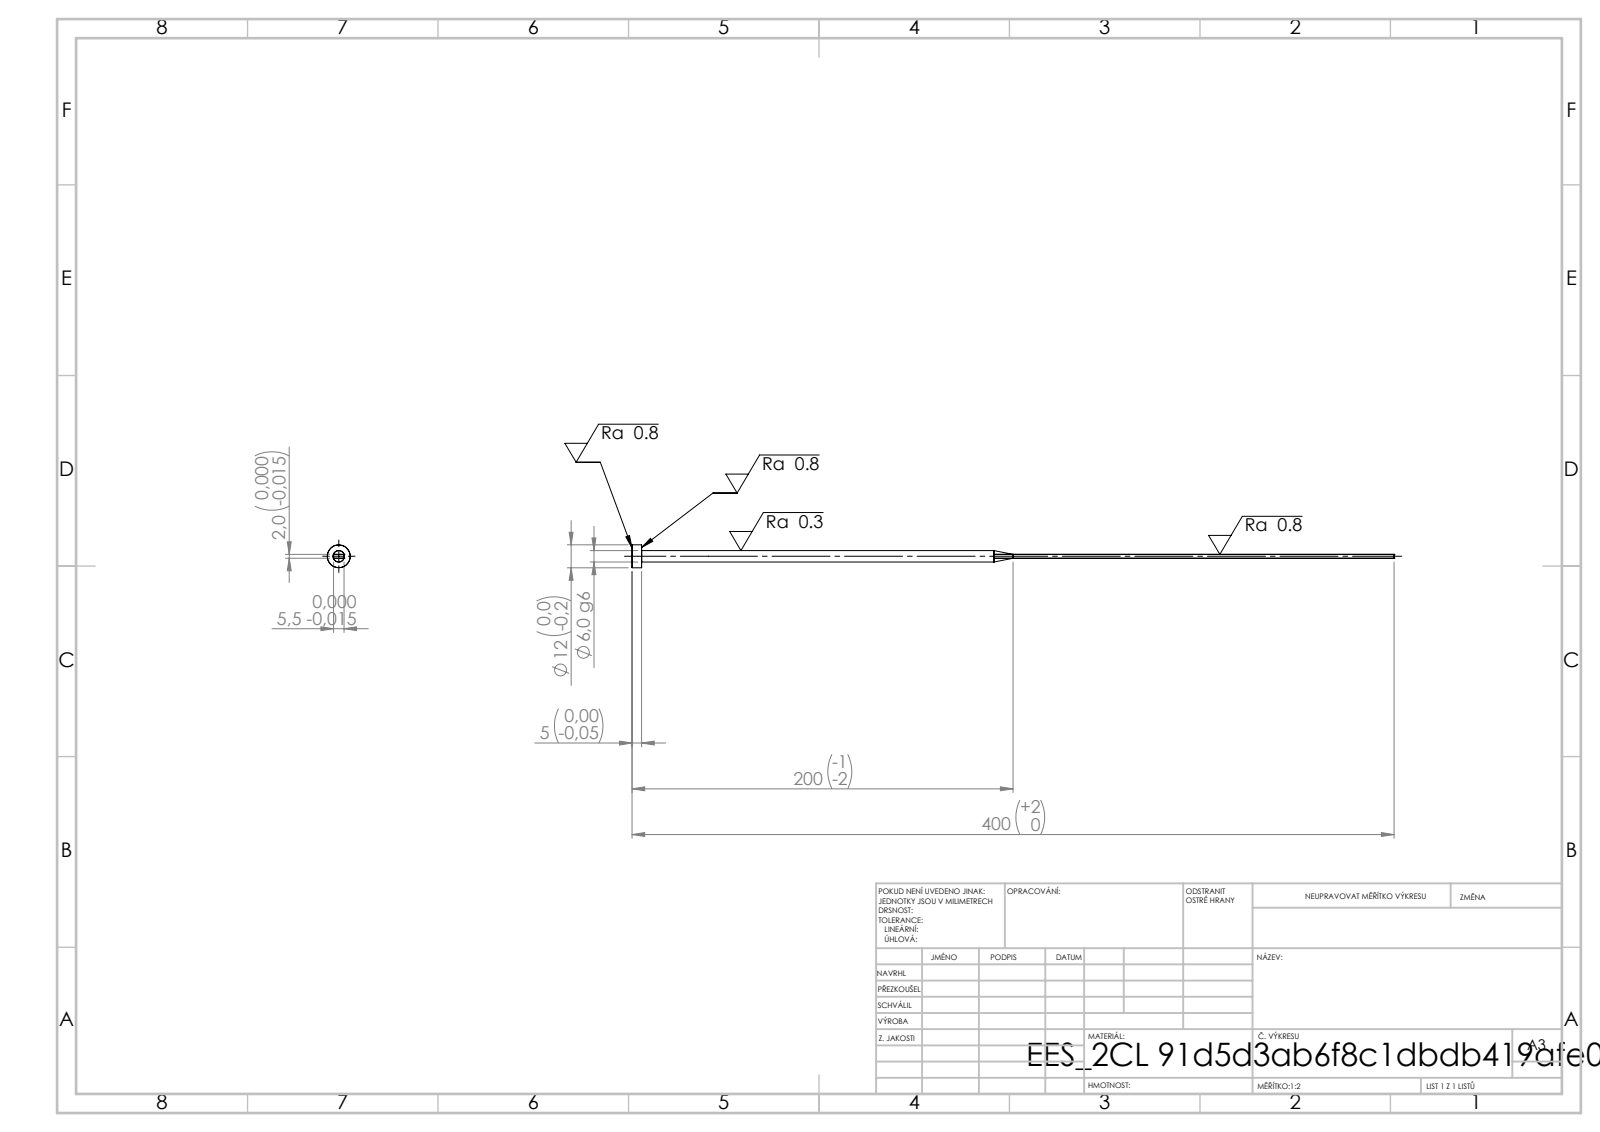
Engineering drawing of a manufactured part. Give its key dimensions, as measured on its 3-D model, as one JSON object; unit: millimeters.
{"step_written_by": "SolidWorks 2019 (CONFIG_CONTROL_DESIGN)", "units": "millimeters", "bodies": {"solids": 1, "faces": 15, "planar": 7, "cylindrical": 4, "other": 4}, "overall_size": [400, 12, 12], "volume_mm3": 8188, "surface_area_mm2": 7050, "round_bosses_or_shafts": [[12, 1], [6, 1]], "face_to_face_distances": [2, 5.5, 5, 400, 395]}
